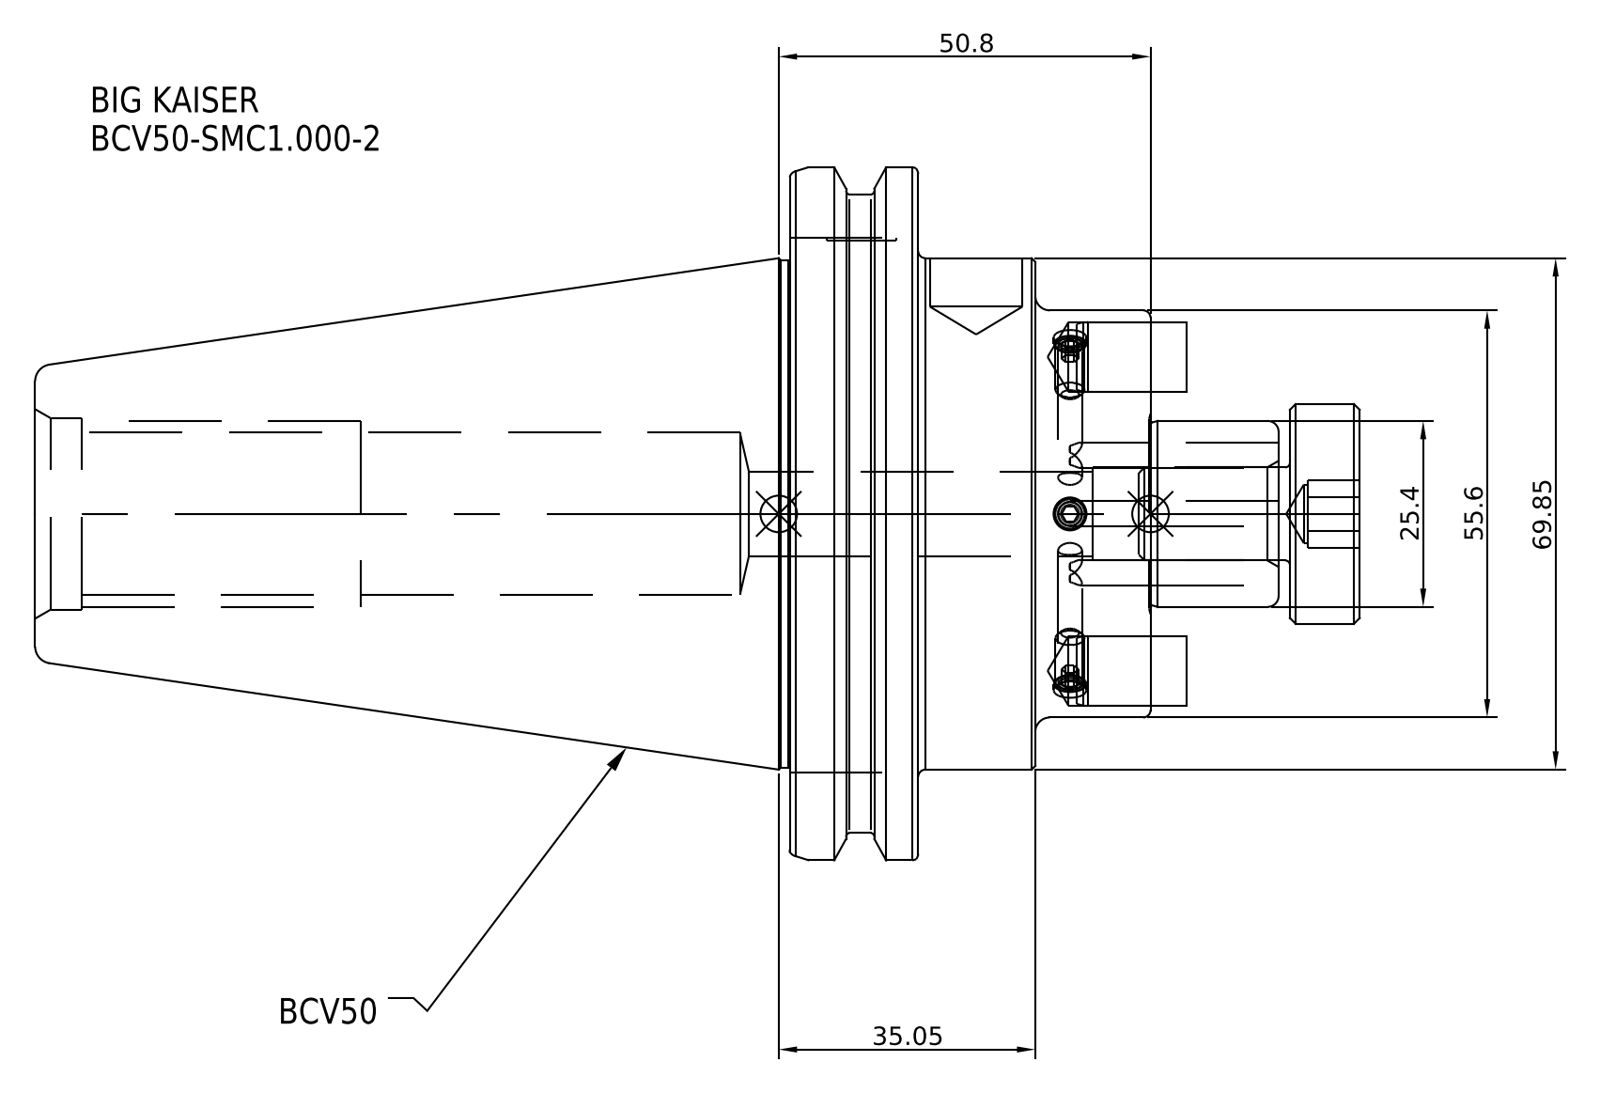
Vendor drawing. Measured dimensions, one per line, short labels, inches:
name: BCV50-SMC1_000-2
written by: SolidWorks 2021 (CONFIG_CONTROL_DESIGN)
unit: in
bodies: 1 solid, 38 faces (18 planar, 14 cylindrical, 6 other)
size: 6.193 × 3.875 × 3.875
volume: 29.3 in³; area: 69.25 in²
holes: 1× ⌀0.453
bosses: 1× ⌀3.875, 1× ⌀3.594, 1× ⌀2.75, 1× ⌀2.189
face distances: 0.691, 1.25, 1.941, 0.62, 0.63, 1.321, 6, 5.38, 4.75, 4.059
